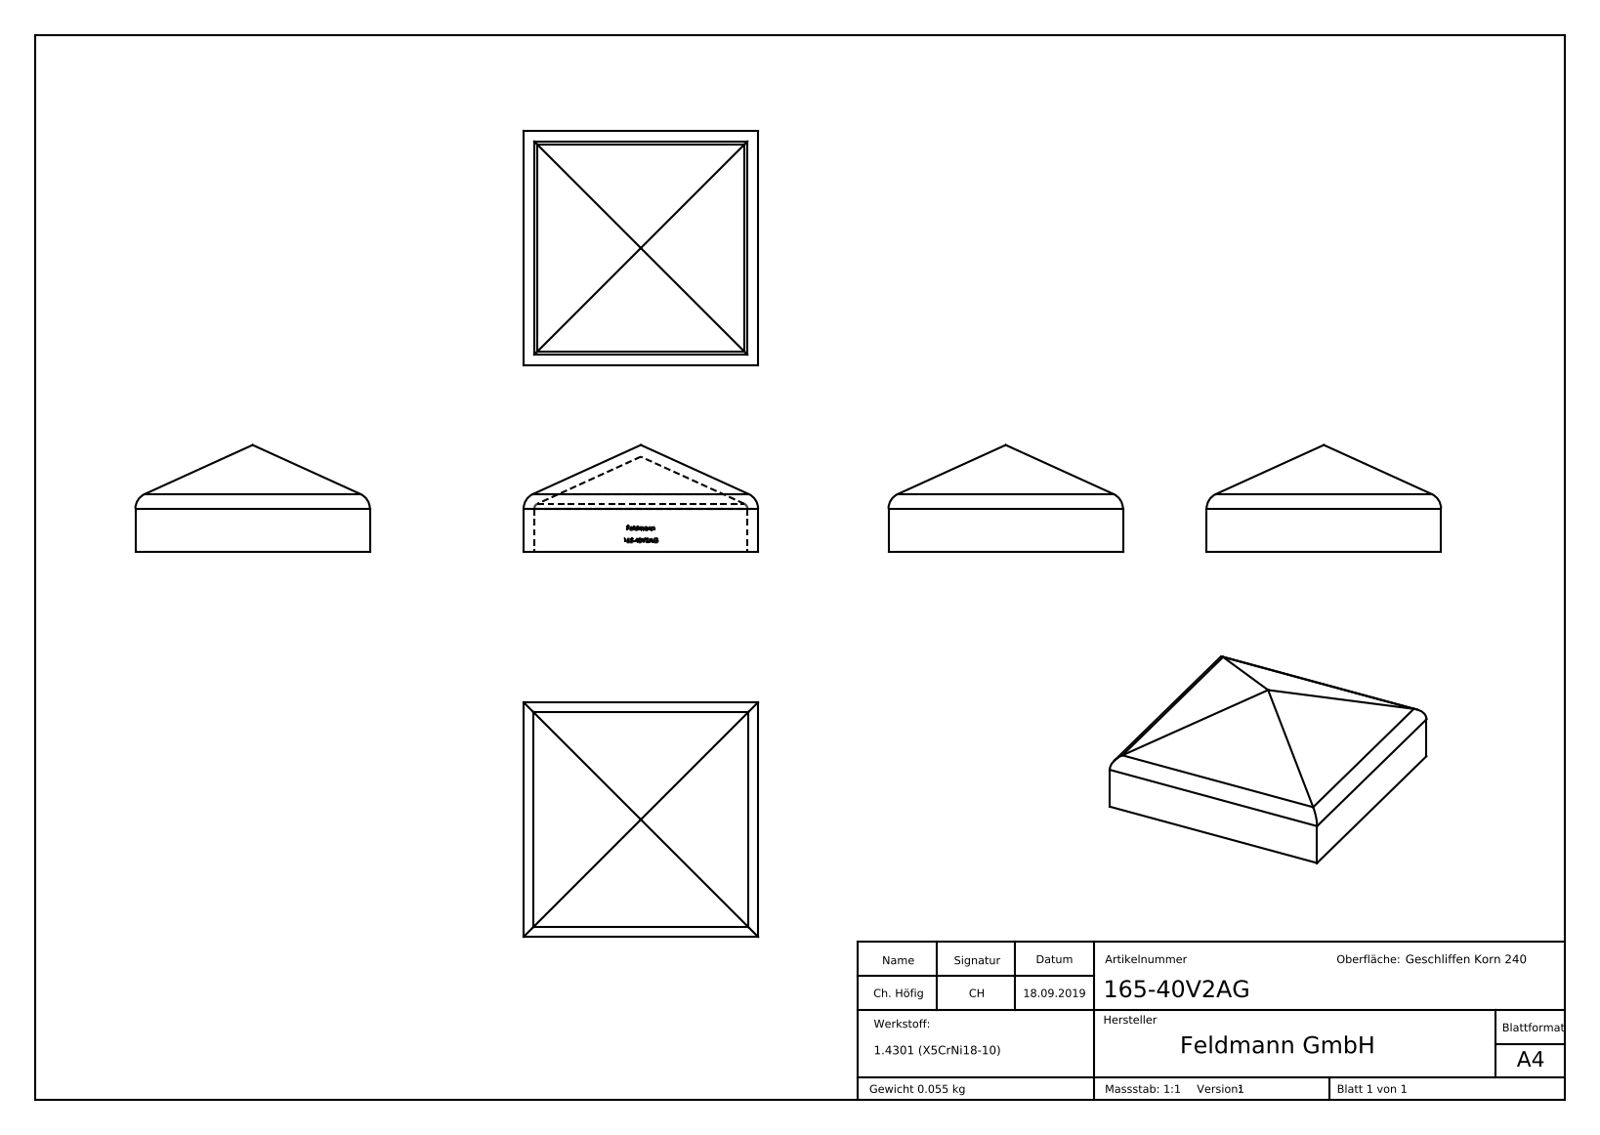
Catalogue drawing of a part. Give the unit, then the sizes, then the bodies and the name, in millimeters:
Units: millimetres
Overall size (bounding box): 44 × 44 × 20
Partial cylindrical surfaces — rounded edges, fillets, slot ends (radius × count): R1 ×4, R3 ×4, R0.1 ×2
Main face-to-face distances: 2, 42, 44, 40, 1.9, 40.1, 42.1, 0.45, 2.33, 0.67
Volume: 6 926 mm³ · Surface area: 7 279 mm²
Bodies: 1 solid, 257 faces (156 planar, 12 cylindrical, 89 other)
Part name (STEP PRODUCT): 165-40V2AG
STEP written by: SolidWorks 2015 (CONFIG_CONTROL_DESIGN)
